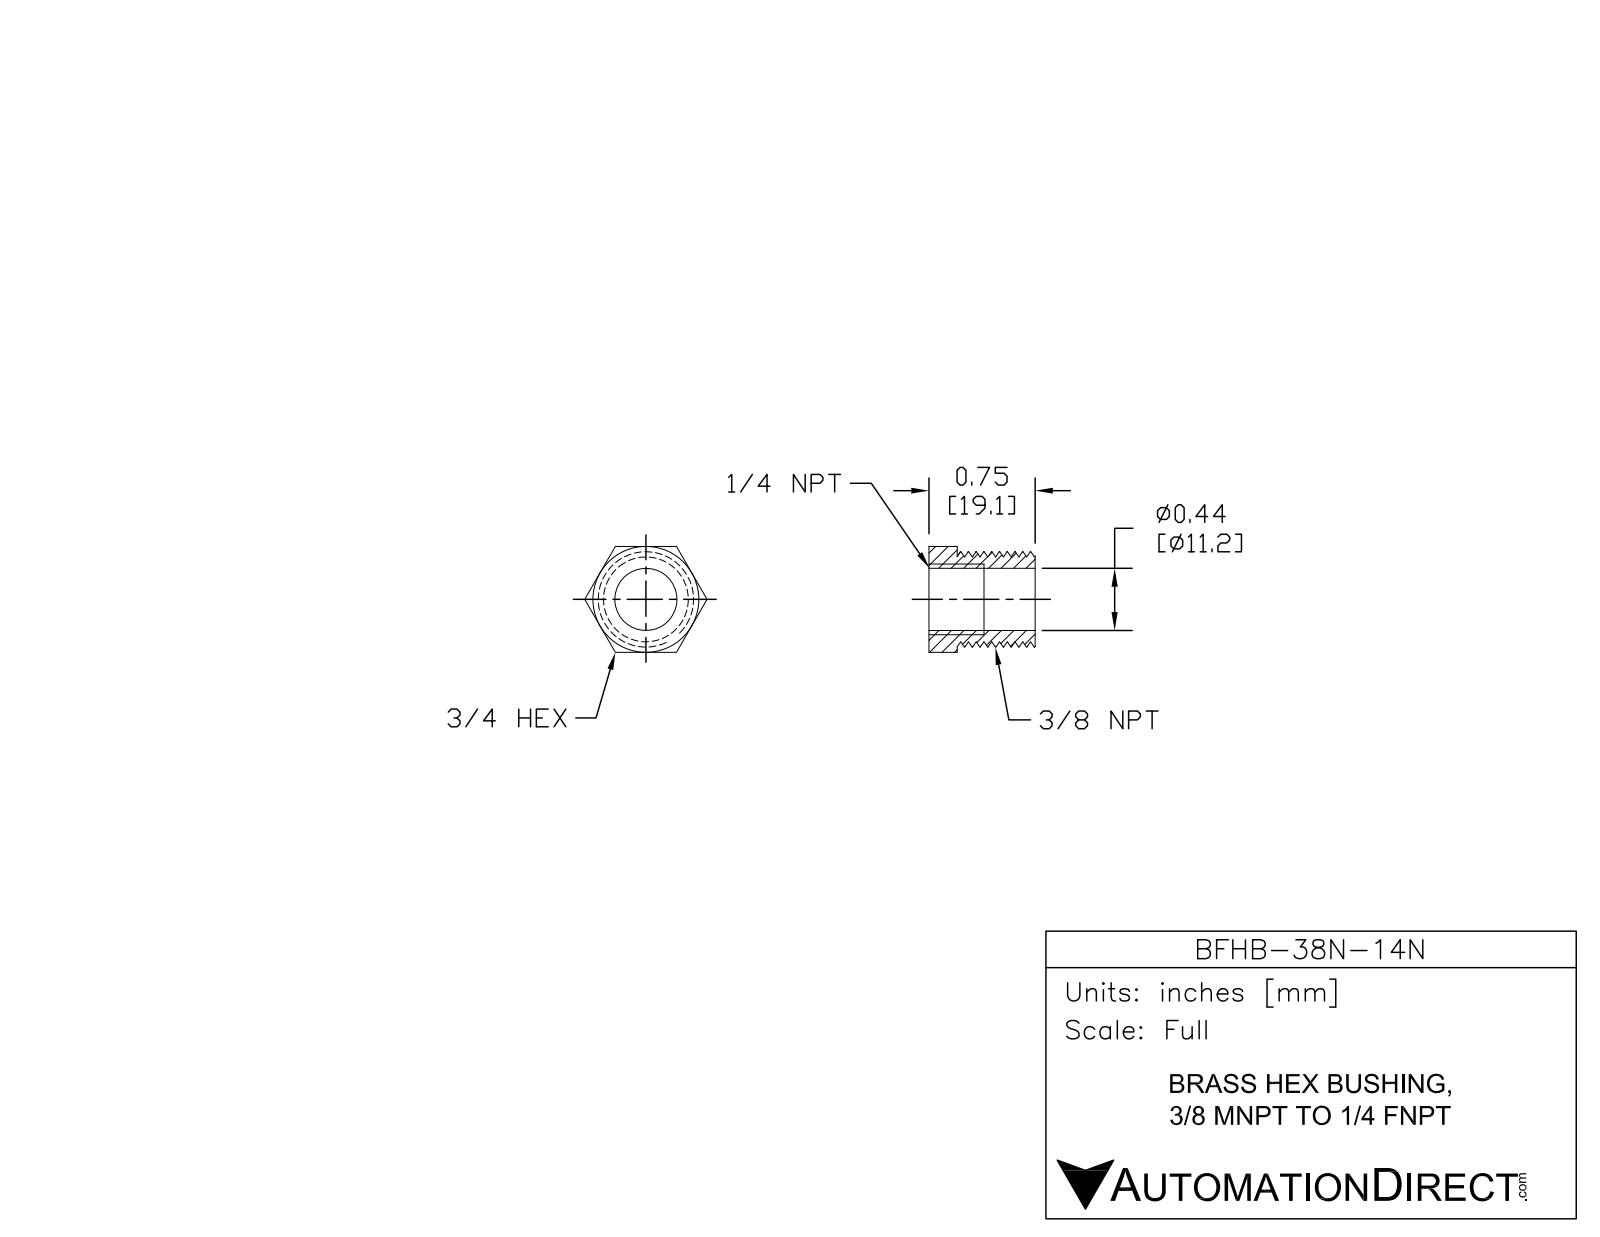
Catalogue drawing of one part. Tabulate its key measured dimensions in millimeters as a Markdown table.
| quantity | value |
| --- | --- |
| part name | BFHB-38N-14N |
| STEP written by | SolidWorks 2015 (CONFIG_CONTROL_DESIGN) |
| units | millimeters |
| bodies | 1 solid, 49 faces (10 planar, 23 cylindrical, 16 other) |
| overall size | 22 × 19.1 × 19.1 |
| volume | 2 620 mm³ |
| surface area | 2 646 mm² |
| round holes (diameter × count) | 11.2 × 1 |
| round bosses / shafts (diameter × count) | 17.1 × 1 |
| main face-to-face distances | 19.1, 19.1, 5.1, 14, 19.1 |
